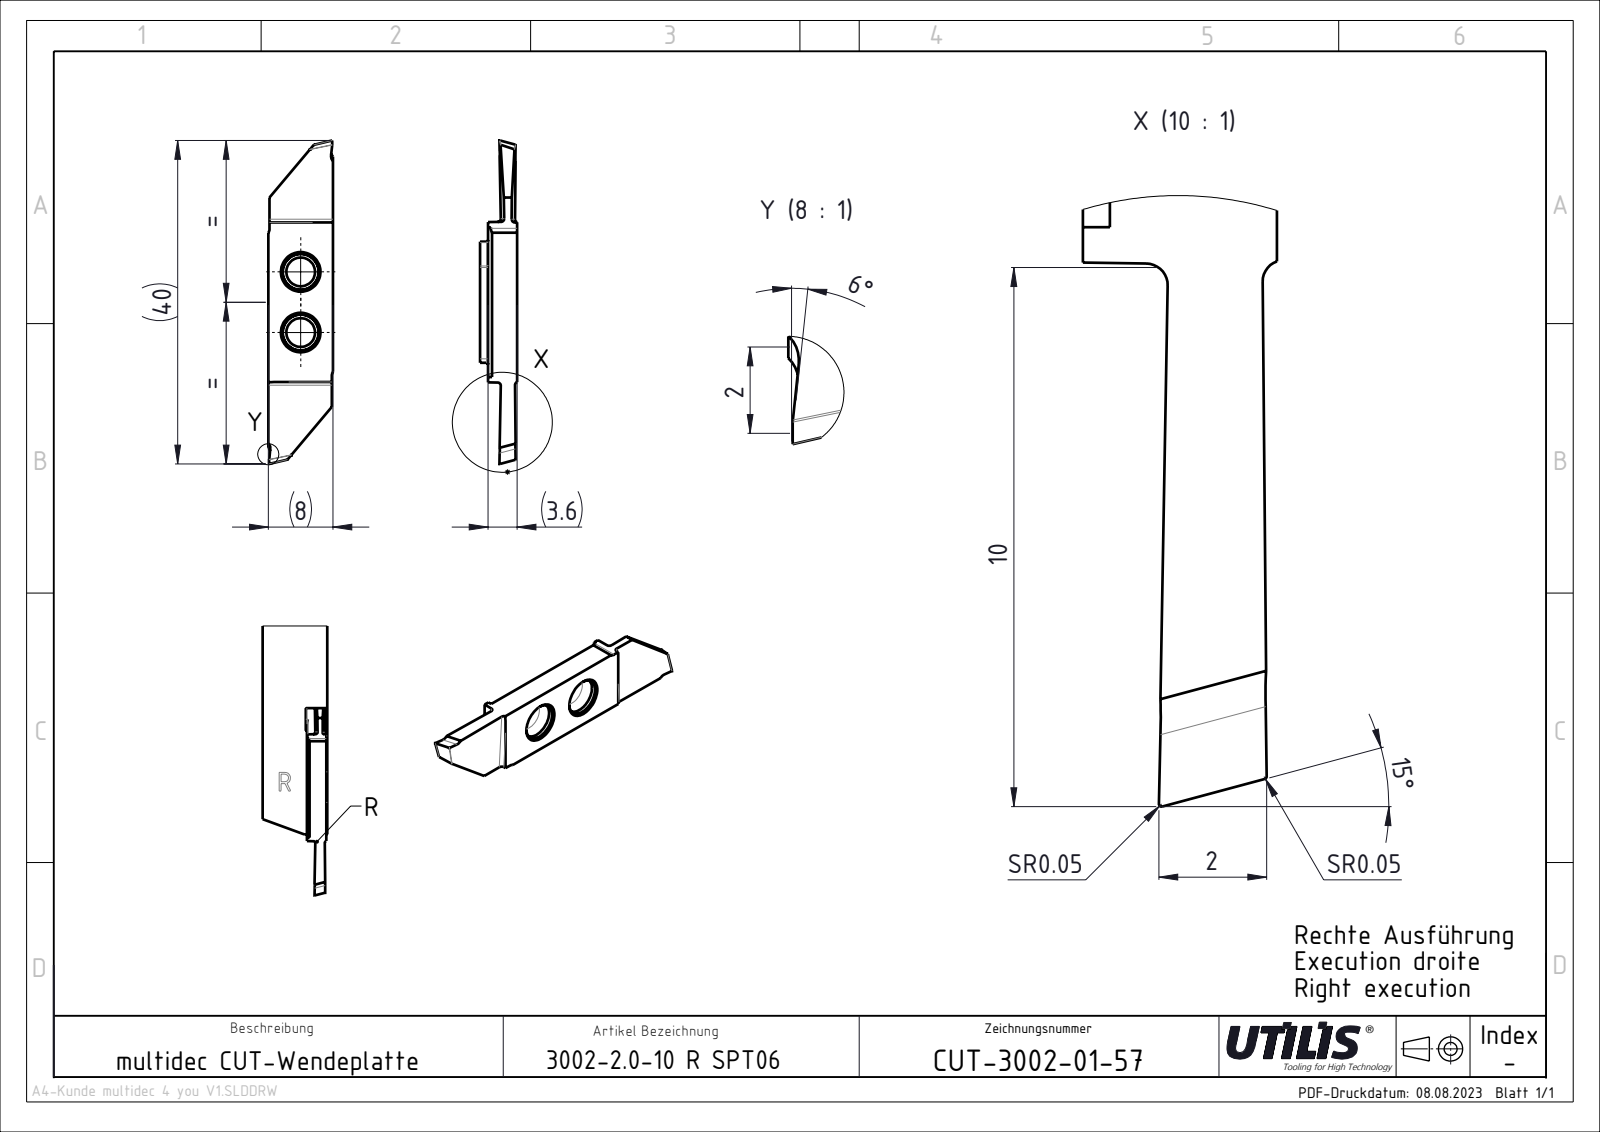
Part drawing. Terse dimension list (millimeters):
name: CUT-3002 SPT; ASME Y14.5
written by: SolidWorks 2023 SP4 || FormatWorks Professional (AP242_MANAGED_MODEL_BASED_3D_ENGINEERING_MIM_LF)
unit: mm
bodies: 1 solid, 36 faces (22 planar, 14 cylindrical, 0 other)
size: 40 × 8 × 3.6
volume: 708 mm³; area: 835 mm²
holes: 2× ⌀3.55
rounds: 4× R0.4, 2× R1
face distances: 3.6, 8, 22.54, 7.85, 7.7, 18.5
hole spacings: 7.49
